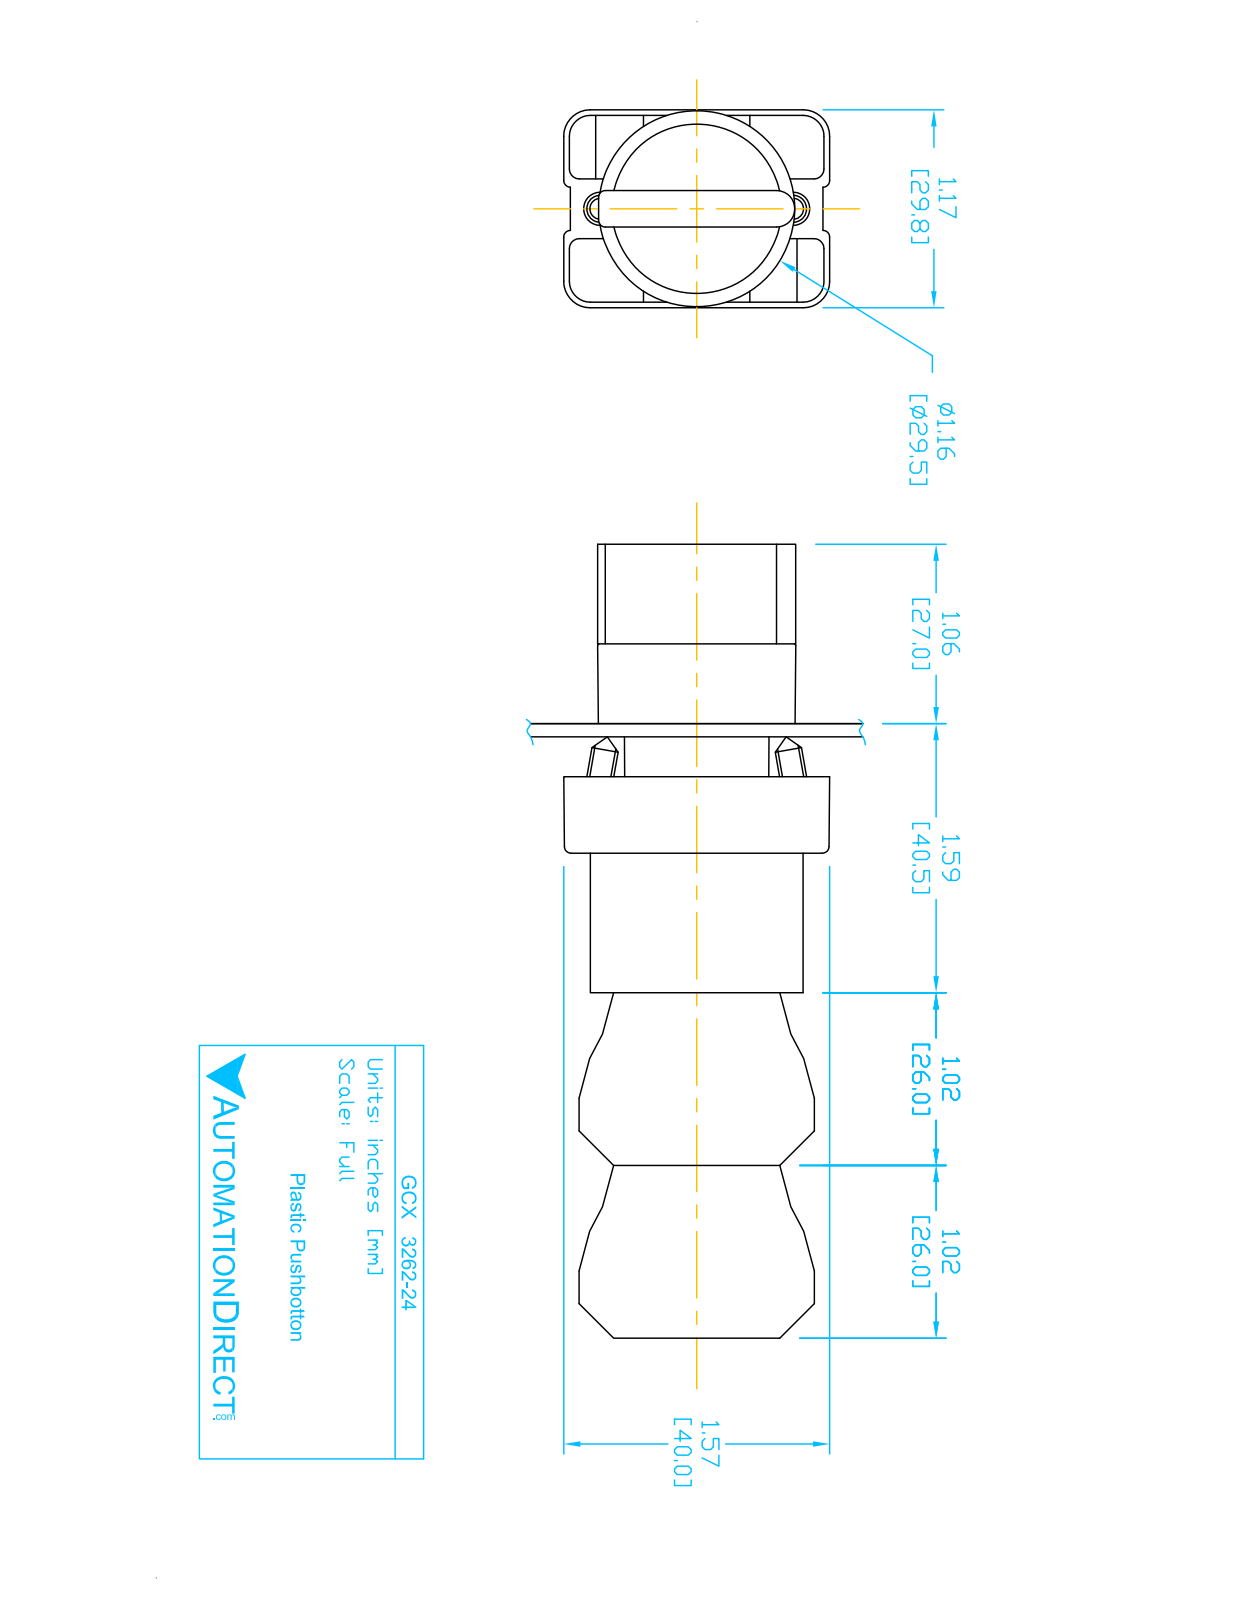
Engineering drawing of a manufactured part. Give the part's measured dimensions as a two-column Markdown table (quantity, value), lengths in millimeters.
| quantity | value |
| --- | --- |
| part name | ECX1050; ecx1040; GCX3262 OPERATOR; GCX3262-24 (+2 more) |
| STEP written by | SolidWorks 2016 (AUTOMOTIVE_DESIGN) |
| units | millimeters |
| bodies | 11 solids, 724 faces (488 planar, 193 cylindrical, 43 other) |
| overall size | 118.8 × 40.2 × 29.9 |
| volume | 77 850 mm³ |
| surface area | 38 210 mm² |
| round holes (diameter × count) | 2 × 4, 2.2 × 2, 3.1 × 2, 3.3 × 2, 5 × 1, 11.9 × 1, 22.3 × 1, 22.6 × 1, 26 × 1 |
| round bosses / shafts (diameter × count) | 4 × 4, 29.8 × 1, 25.5 × 1, 24 × 1, 21.7 × 1, 19.8 × 1, 12.8 × 1 |
| partial cylindrical surfaces (radius × count) | 1.5 × 24, 1 × 12, 3.1 × 12, 4 × 12, 1 × 9, 0.5 × 2, 1.6 × 2, 2 × 2 |
| main face-to-face distances | 14.7, 15.1, 26, 29.7, 0.4, 21, 47, 77.3, 51.3, 30.3 |
| hole center spacings | 6, 25.5, 24.7, 12, 13.7, 13.8, 27.5, 12.3 |
